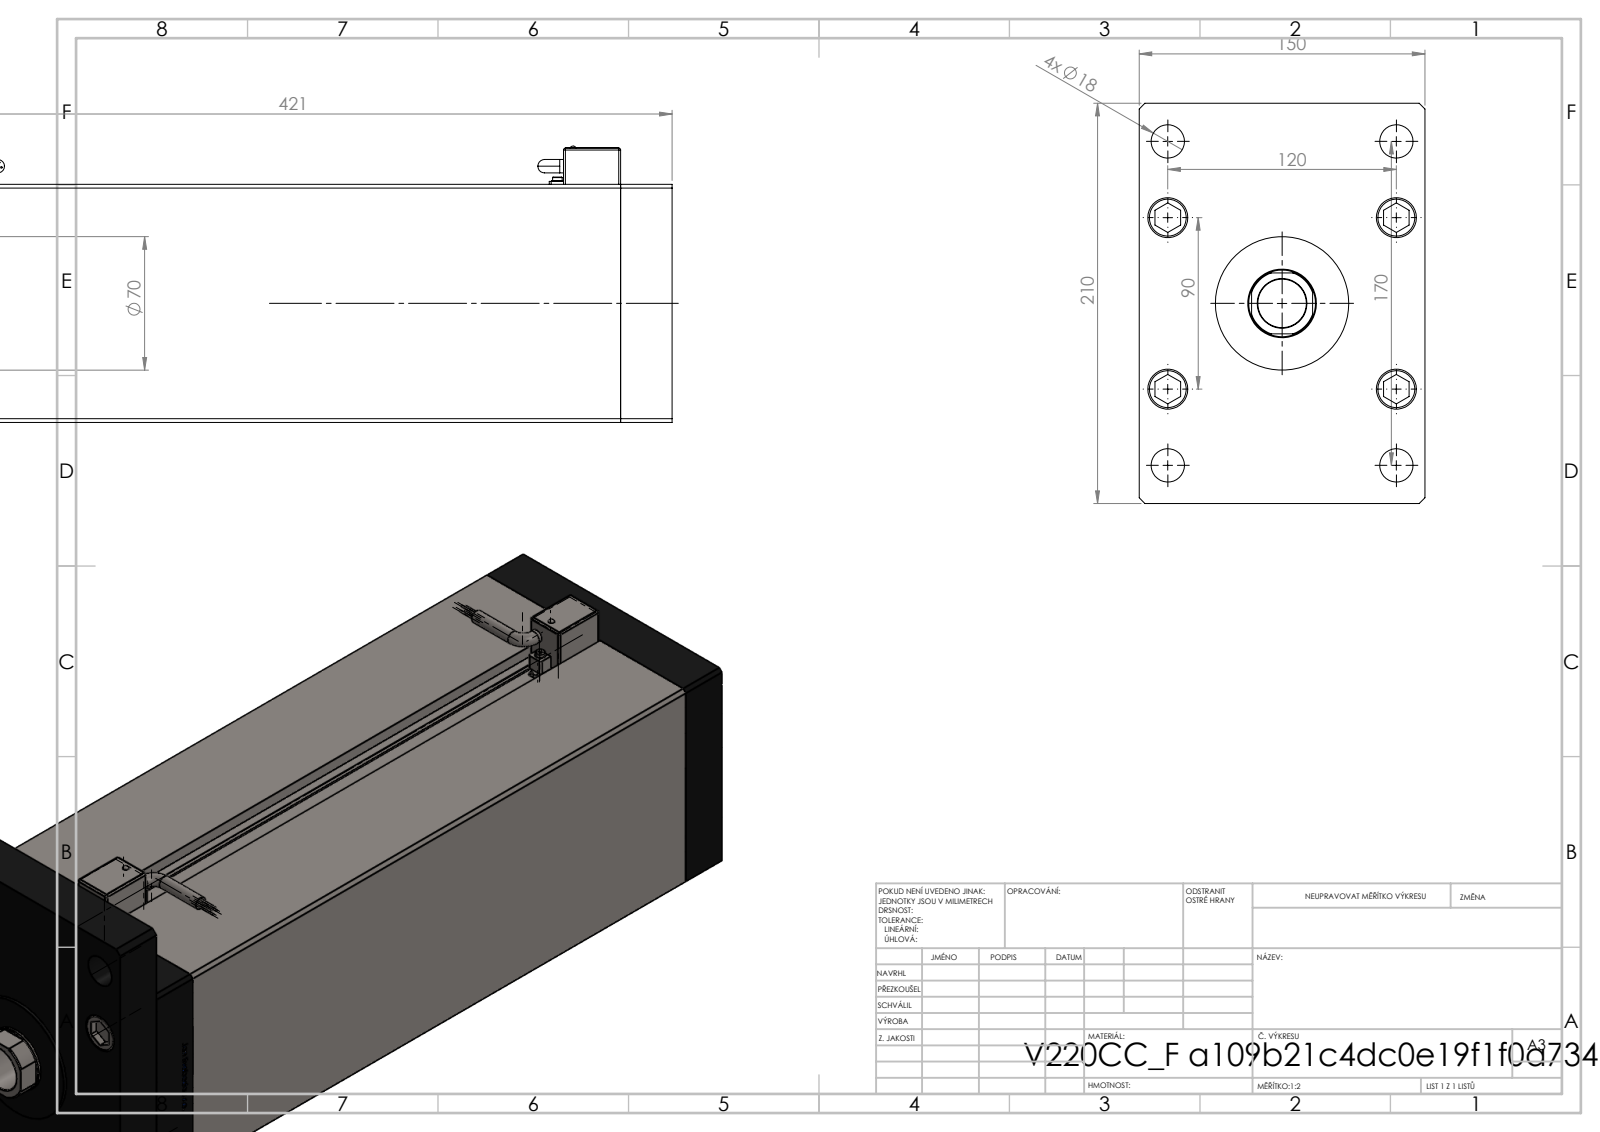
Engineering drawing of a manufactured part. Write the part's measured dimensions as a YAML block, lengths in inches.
part_name: "Magnetic_Switch_MSU4; V220C_VC_F; V220C_FRONT_F; V220C_F_MIDDLE (+3 more)"
step_written_by: "SolidWorks 2019 (CONFIG_CONTROL_DESIGN)"
units: inches
bodies: {solids: 21, faces: 1502, planar: 591, cylindrical: 269, other: 642}
overall_size: [18.228, 8.268, 5.906]
volume: 446.3
surface_area: 1037
round_holes:
  - {diameter: 0.689, count: 9}
  - {diameter: 0.866, count: 5}
  - {diameter: 0.63, count: 4}
  - {diameter: 0.827, count: 4}
  - {diameter: 0.142, count: 2}
  - {diameter: 0.197, count: 2}
  - {diameter: 0.276, count: 2}
  - {diameter: 1.004, count: 1}
  - {diameter: 1.417, count: 1}
  - {diameter: 1.476, count: 1}
round_bosses_or_shafts:
  - {diameter: 0.315, count: 9}
  - {diameter: 0.033, count: 8}
  - {diameter: 0.827, count: 5}
  - {diameter: 0.276, count: 4}
  - {diameter: 0.236, count: 2}
  - {diameter: 0.138, count: 2}
  - {diameter: 0.098, count: 2}
  - {diameter: 3.15, count: 1}
partial_cylinders:
  - {radius: 0.039, count: 24}
  - {radius: 0.157, count: 4}
  - {radius: 0.037, count: 2}
  - {radius: 0.689, count: 1}
face_to_face_distances: [1.063, 5.906, 4.921, 15.512, 16.575, 14.449, 2.126, 17.638, 0.256, 1.319]
hole_center_spacings: [2.008, 1.575, 2.953, 4.096, 4.724, 4.98, 5.118, 6.965]
